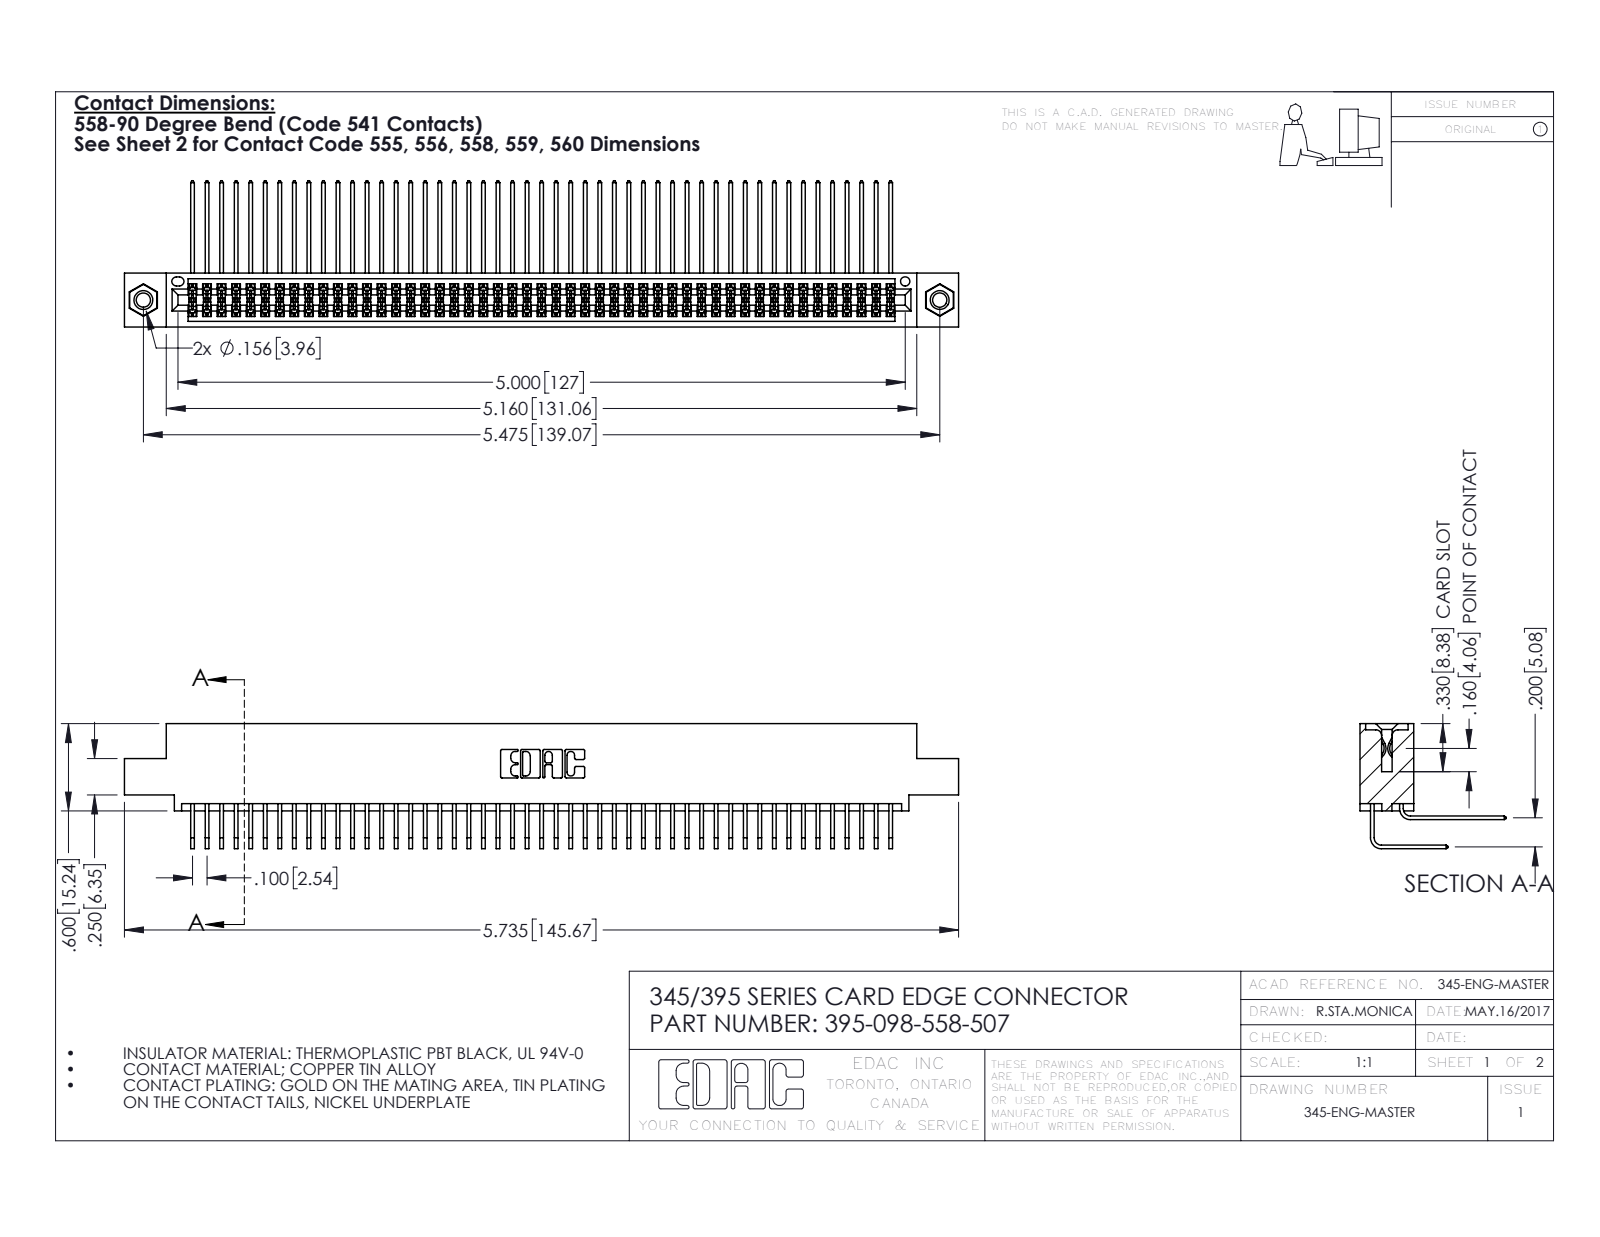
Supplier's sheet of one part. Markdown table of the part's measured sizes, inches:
| quantity | value |
| --- | --- |
| part name | 345 Part_0.110 Offset - 0.156 Dia-TI; 345-292-001_558 559 Tail - 1; 345-292-001_558 Tail - 2; 345-250-001_345-250-005-103 (+1 more) |
| STEP written by | SolidWorks 2016 (CONFIG_CONTROL_DESIGN) |
| units | inches |
| bodies | 101 solids, 5286 faces (3546 planar, 1724 cylindrical, 16 other) |
| overall size | 5.735 × 1.005 × 0.859 |
| volume | 0.897 in³ |
| surface area | 38.18 in² |
| round holes (diameter × count) | 0.098 × 2, 0.125 × 2, 0.156 × 2, 0.064 × 1 |
| round bosses / shafts (diameter × count) | 0.155 × 2 |
| partial cylindrical surfaces (radius × count) | 0.006 × 148, 0.01 × 22, 0.007 × 6, 0.031 × 6, 0.026 × 3, 0.014 × 2, 0.019 × 2, 0.022 × 2 |
| main face-to-face distances | 0.072, 0.298, 0.2, 0.37, 0.098, 0.272, 0.025, 0.225, 0.025, 0.175 |
| hole center spacings | 0.27, 5.239, 5.475 |
